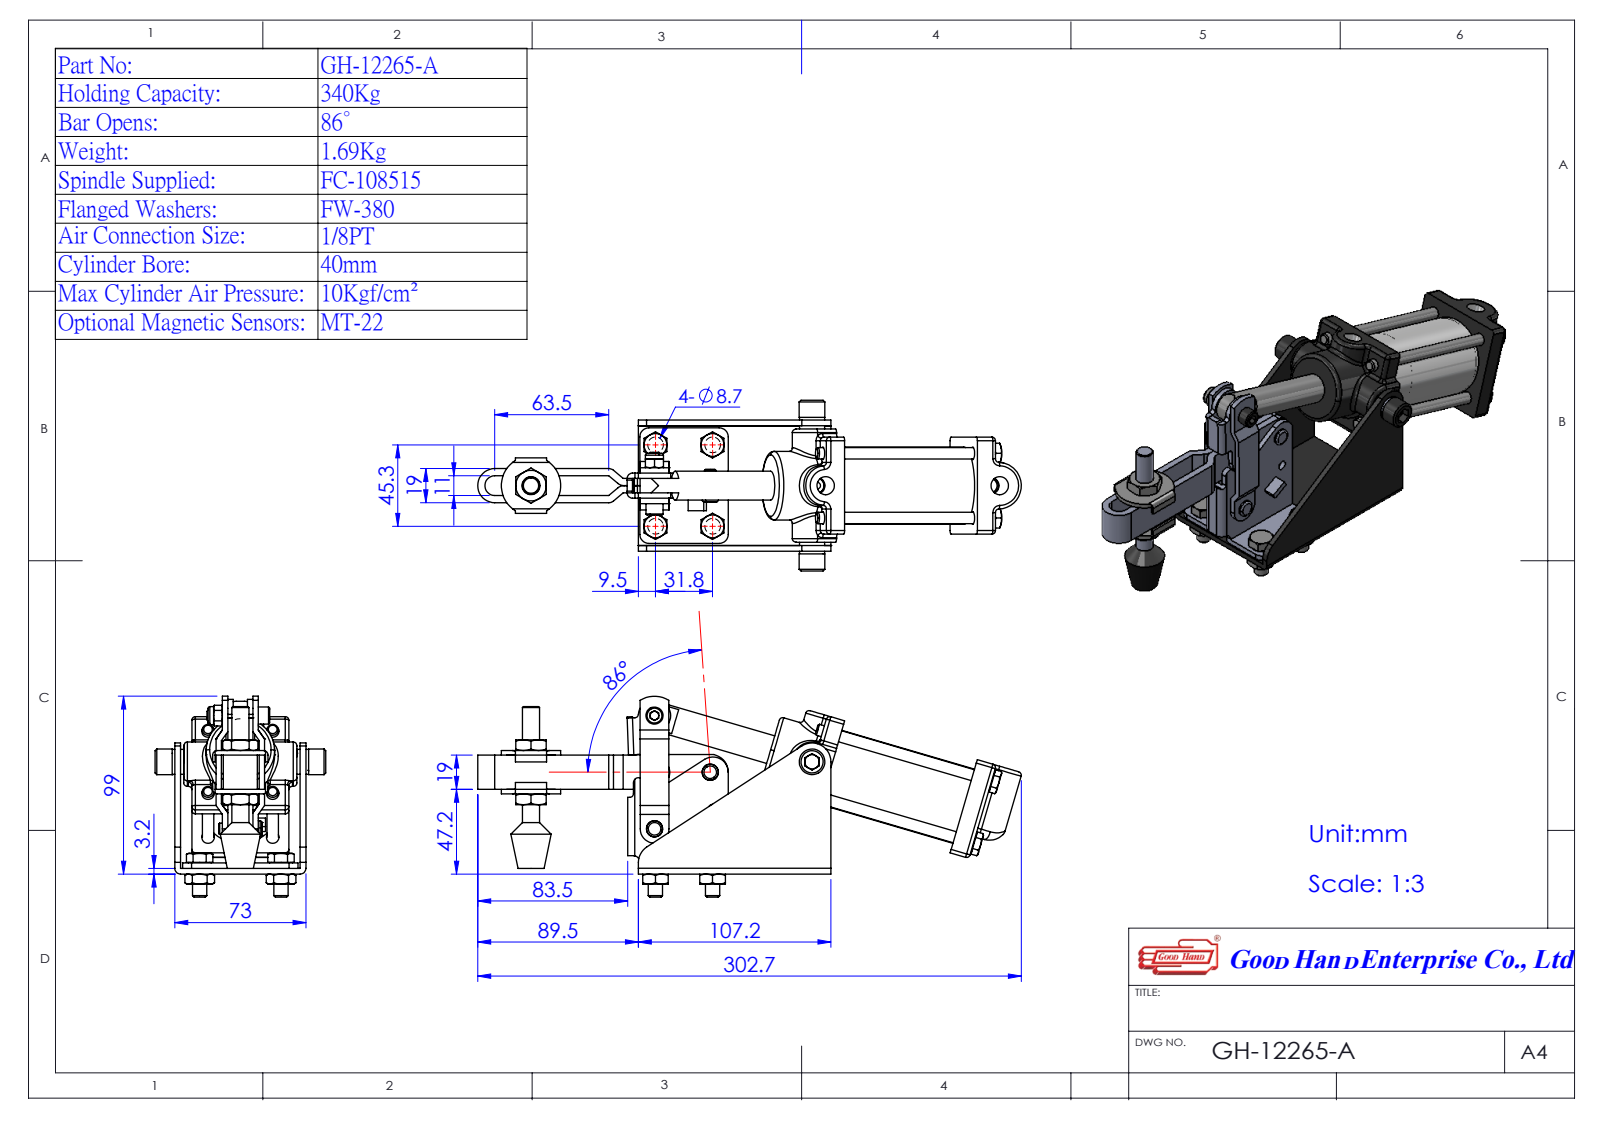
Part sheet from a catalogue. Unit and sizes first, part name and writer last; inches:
Units: inches
Overall size (bounding box): 11.918 × 4.404 × 3.372
Round holes (diameter × count): ⌀0.217 ×4, ⌀0.311 ×2, ⌀0.189 ×1, ⌀0.63 ×1, ⌀1.654 ×1
Round bosses / shafts (diameter × count): ⌀0.313 ×5, ⌀0.5 ×4, ⌀0.25 ×4, ⌀0.438 ×2, ⌀1.693 ×1, ⌀1.654 ×1, ⌀1.504 ×1, ⌀0.63 ×1
Partial cylindrical surfaces — rounded edges, fillets, slot ends (radius × count): R0.079 ×36, R0.039 ×4, R0.1 ×4, R0.157 ×4, R0.197 ×4, R0.118 ×3, R0.126 ×2, R0.197 ×2
Main face-to-face distances: 0.126, 0.118, 1.28, 1.594, 0.433, 2.748, 1.154, 1.469, 0.157, 1.161
Hole centre spacings: 1.241, 1.181, 1.74, 1.742, 2.244, 2.48, 3.421, 3.6
Volume: 19.44 in³ · Surface area: 229.3 in²
Bodies: 7 solids, 871 faces (367 planar, 247 cylindrical, 257 other)
Part name (STEP PRODUCT): Group8^GH-12265-A(簡化)-1; Group7^GH-12265-A(簡化)-1; 12265A-CYLINDER-1^GH-12265-A(簡化)-1; Group2^GH-12265-A(簡化) (+4 more)
STEP written by: SolidWorks 2016 (AUTOMOTIVE_DESIGN)
